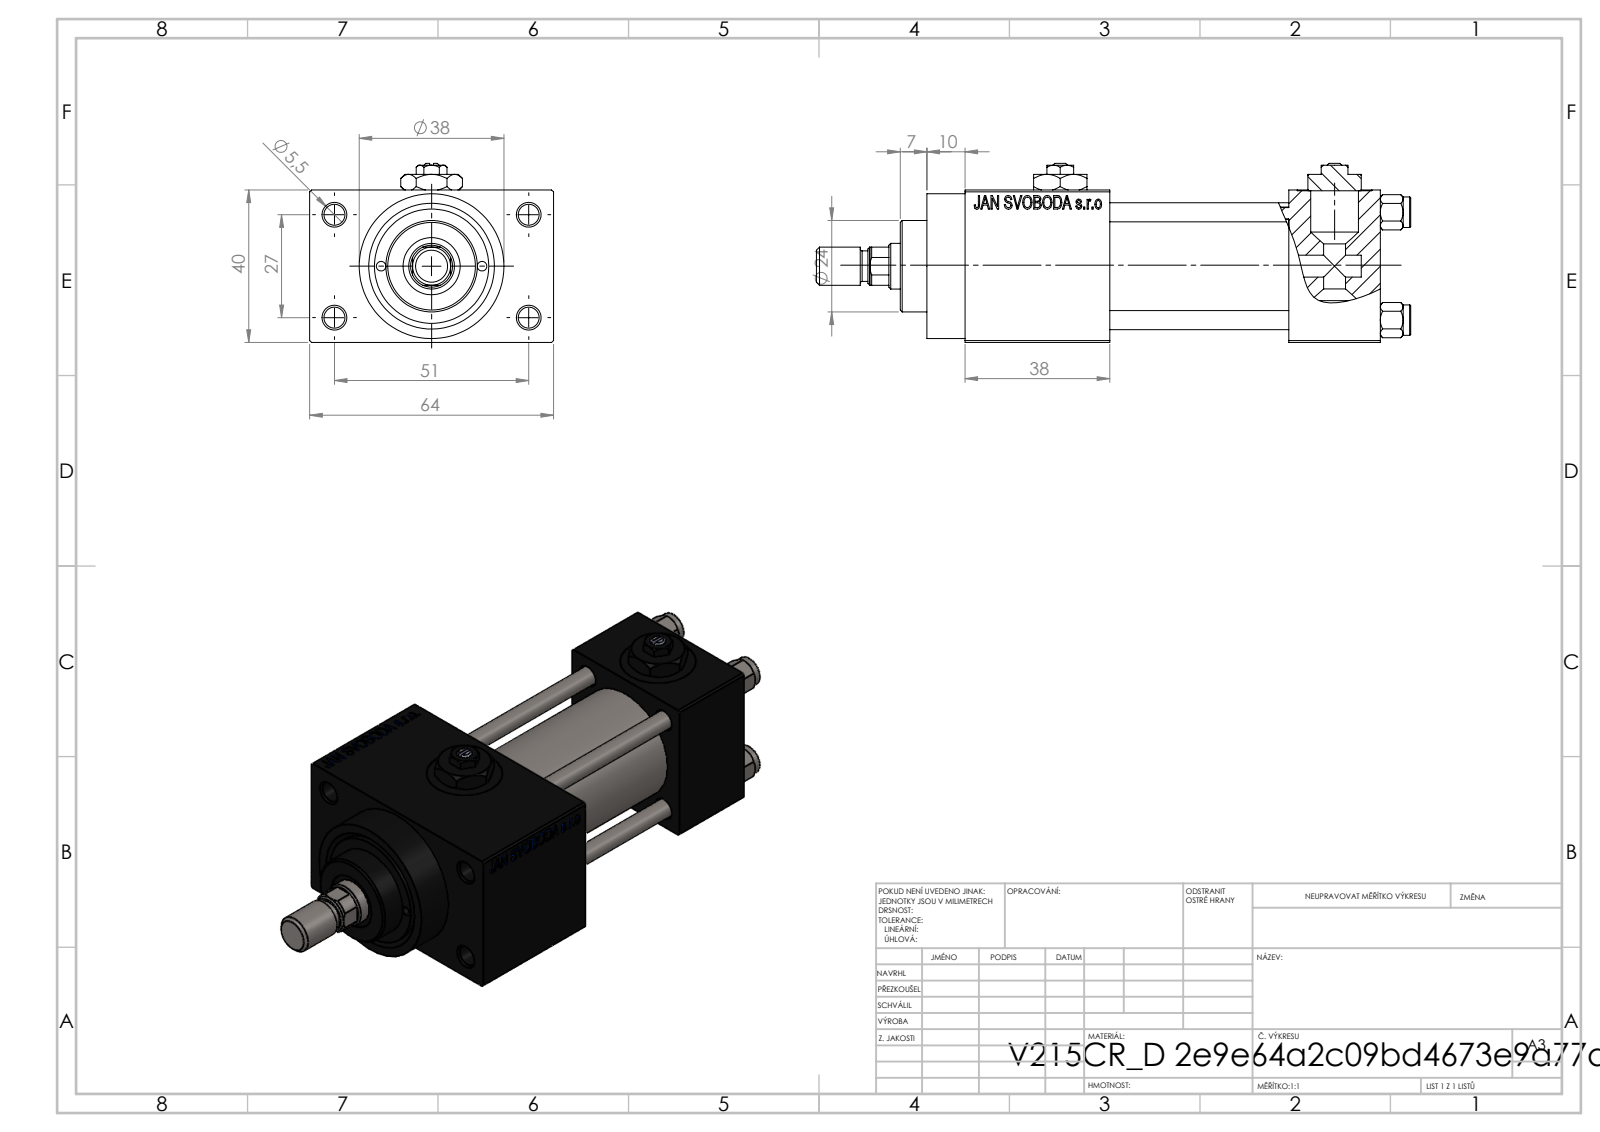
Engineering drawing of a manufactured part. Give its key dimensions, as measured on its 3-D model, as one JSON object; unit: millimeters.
{"part_name": "V215CR_VCP_D; V215CR_D_TYCINKA; Zatka_pro_OIL_PORT; V215CR_D_Body (+3 more)", "step_written_by": "SolidWorks 2019 (CONFIG_CONTROL_DESIGN)", "units": "millimeters", "bodies": {"solids": 14, "faces": 1224, "planar": 548, "cylindrical": 108, "other": 568}, "overall_size": [156, 64, 47], "volume_mm3": 175086, "surface_area_mm2": 63924, "round_holes": [[5, 4], [5.5, 4], [20, 3], [2.5, 2], [7, 2], [13.16, 2], [6.5, 1], [12, 1], [15, 1], [25, 1], [30, 1]], "round_bosses_or_shafts": [[8, 5], [38, 1], [31, 1], [24, 1], [10, 1]], "partial_cylinders_radius": [[5.5, 1]], "face_to_face_distances": [40, 52, 12, 47, 71, 24, 64, 38, 85, 109], "hole_center_spacings": [11.37, 14.18, 18.23, 20.01, 28.3, 28.85, 29.89, 30.84]}
